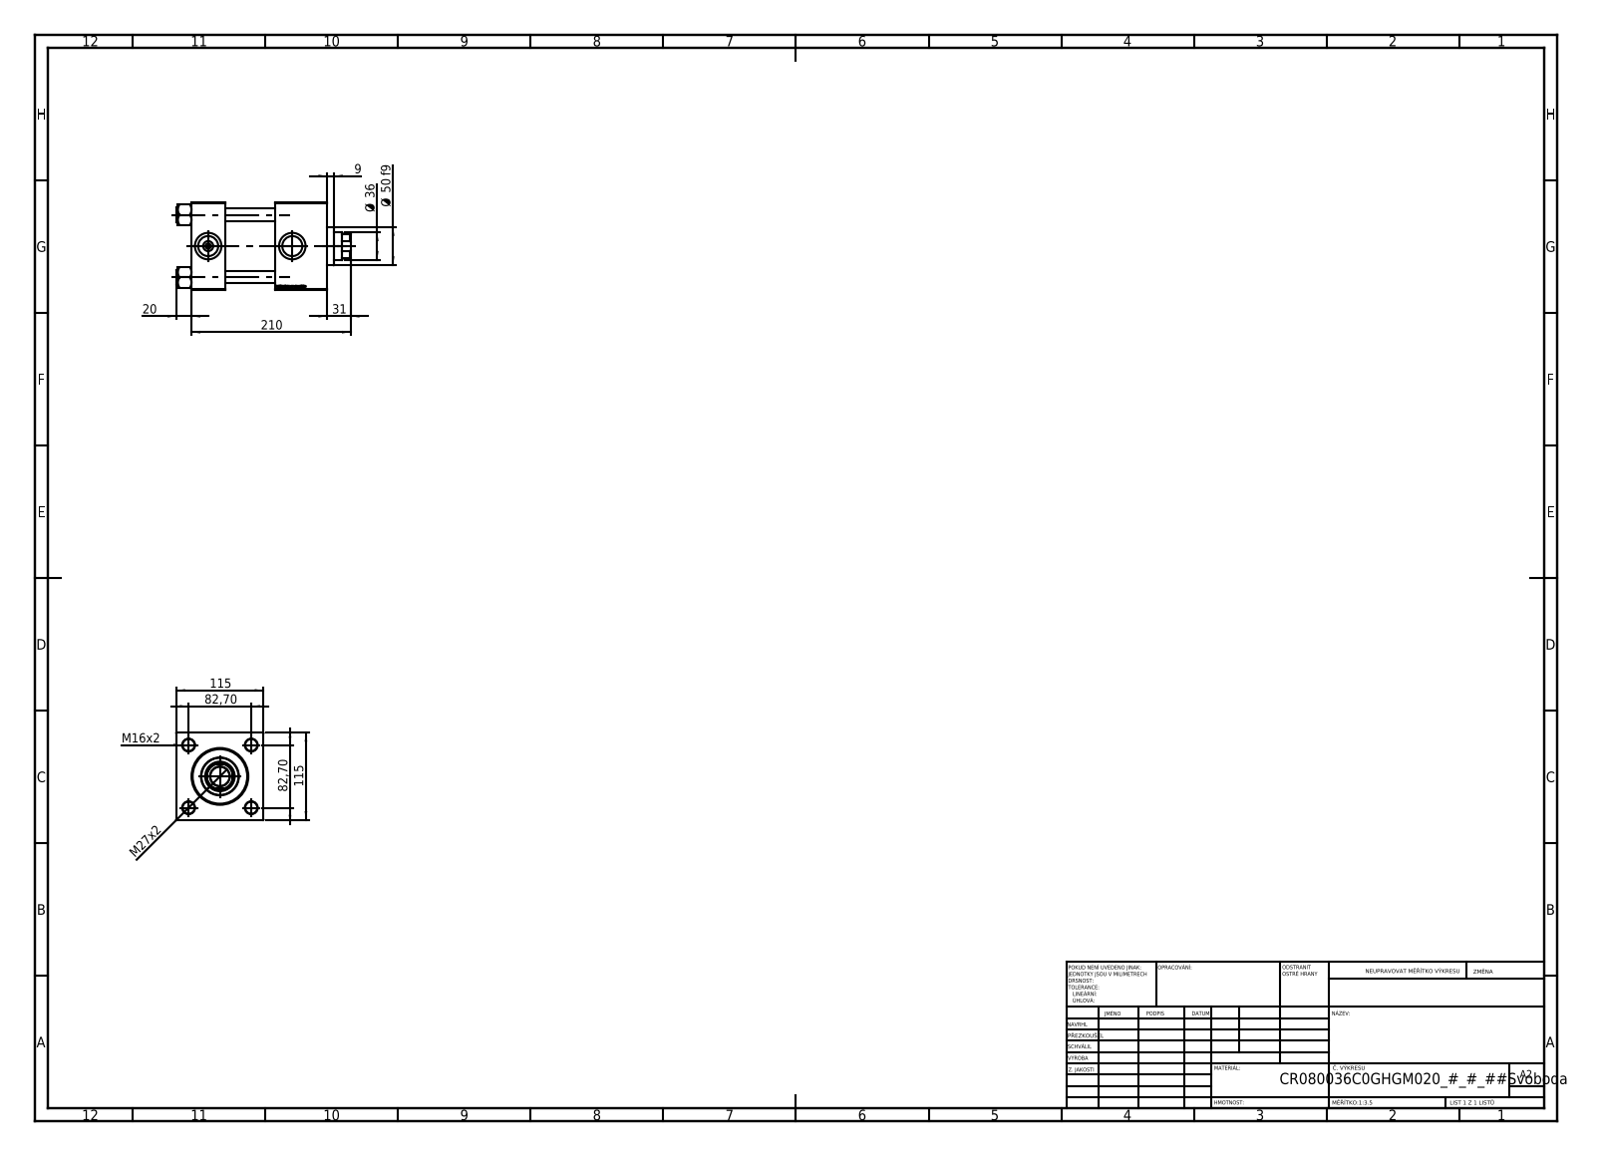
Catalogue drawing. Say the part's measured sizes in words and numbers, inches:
The part is named "V215CR_C_TYCINKA; V215_VC_A; V215CR_C_Body; V215CR_VCP_C (+1 more)". Its 3-D file was written by "SolidWorks 2019 (CONFIG_CONTROL_DESIGN)". It is 11 solids with 1196 faces: 574 planar, 86 cylindrical and 536 other. Overall it measures 9.055 by 4.528 by 4.528 inches. Its volume is 109 cubic inches and its surface area 416.1 square inches. Round holes: 4 of diameter 0.63, 2 of diameter 0.276, 2 of diameter 1.041, 2 of diameter 1.378, 1 of diameter 1.004, 1 of diameter 1.417, 1 of diameter 1.535, 1 of diameter 2.402, 1 of diameter 2.835, 1 of diameter 3.15. Round bosses or shafts: 4 of diameter 0.748, 1 of diameter 3.386, 1 of diameter 1.969. Partial cylindrical surfaces (rounded edges, fillets, slot ends): 1 of radius 0.689. The main face-to-face distances are 4.528, 1.732, 7.047, 5.315, 4.331, 2.598, 2.717, 0.787, 5.917, 4.185. The hole center spacings are 2.302, 3.256, 4.605, 4.37.
